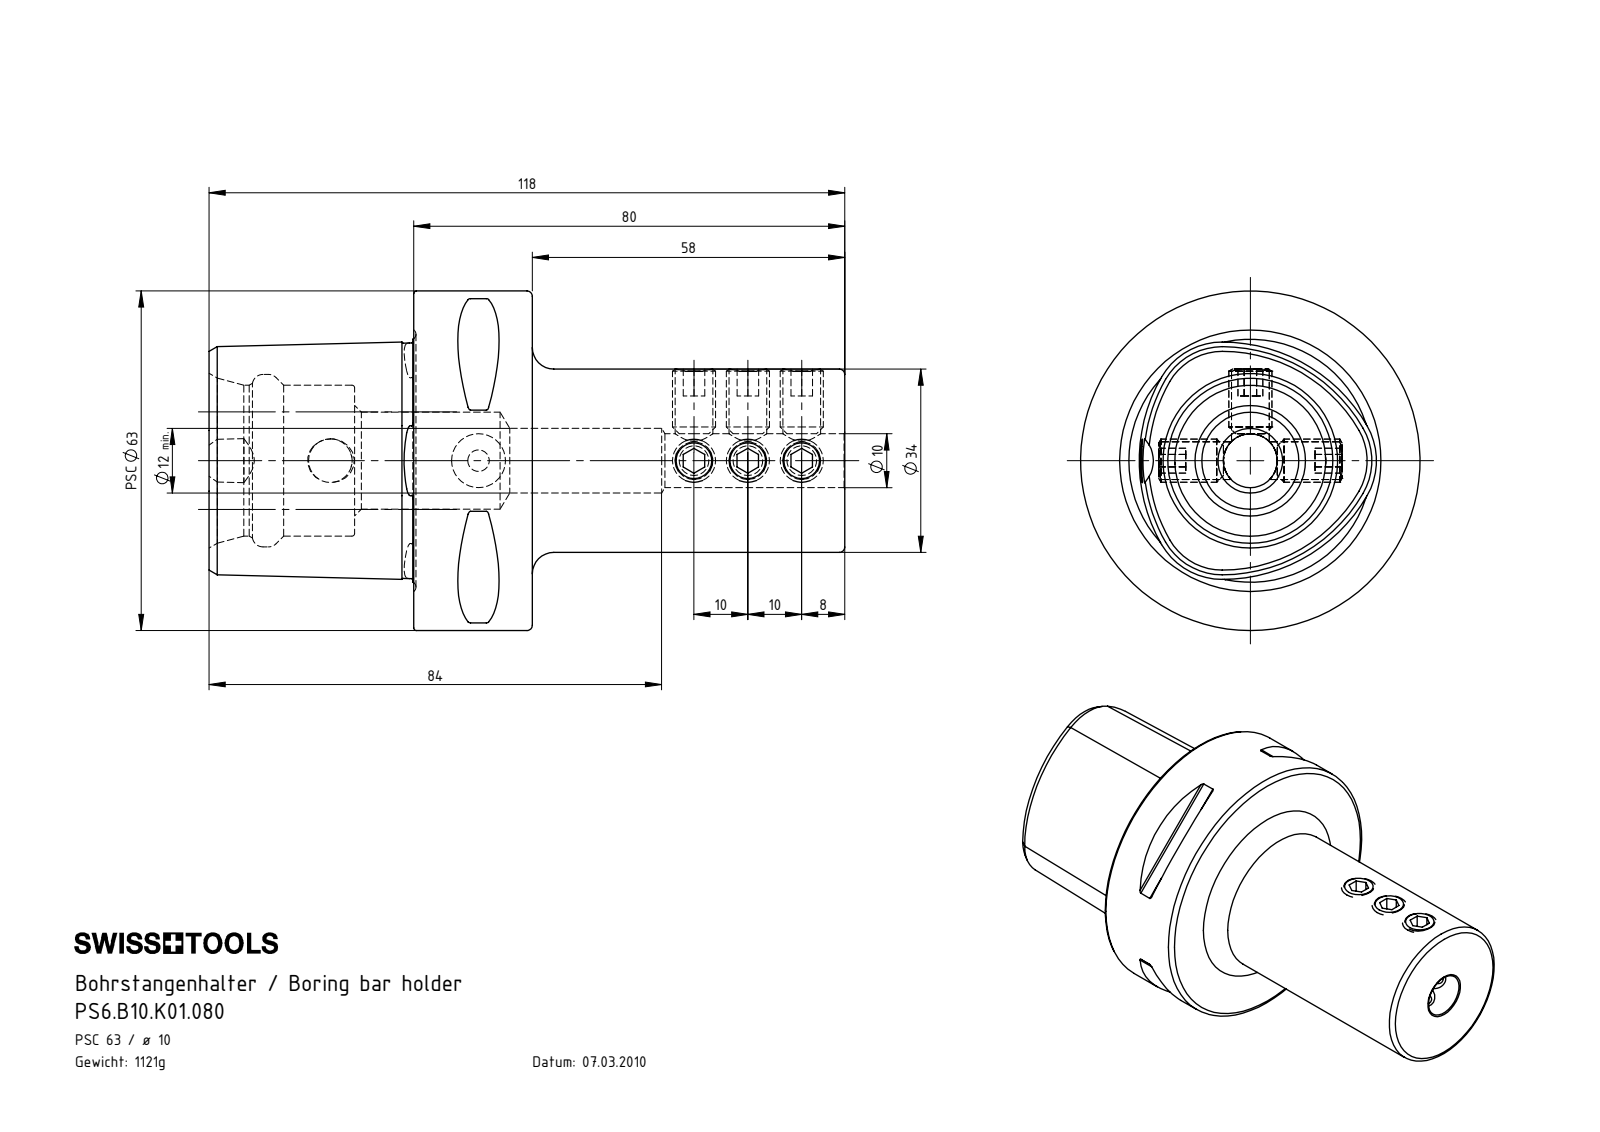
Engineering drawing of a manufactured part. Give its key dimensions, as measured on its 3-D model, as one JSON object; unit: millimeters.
{"part_name": "PS6.B10.K01.080; ISO 4026 - M8 x 12_PreviewCfg; ISO 4026 - M8 x 12; PS6-B10.K01.080_A", "step_written_by": "SolidWorks 2017 (AUTOMOTIVE_DESIGN)", "units": "millimeters", "bodies": {"solids": 10, "faces": 285, "planar": 101, "cylindrical": 67, "other": 117}, "overall_size": [118, 63, 63], "volume_mm3": 143216, "surface_area_mm2": 33576, "round_holes": [[7, 6], [4, 1], [8.1, 1], [10, 1], [12, 1], [18, 1], [28, 1], [32, 1]], "round_bosses_or_shafts": [[8, 6], [63, 1], [34, 1]], "partial_cylinders_radius": [[0.5, 8], [6, 1]], "face_to_face_distances": [22, 80, 58, 38, 60, 118, 5, 10, 4, 24.88], "hole_center_spacings": [10, 20, 27.5, 40, 50, 60, 67.5, 77.5]}
